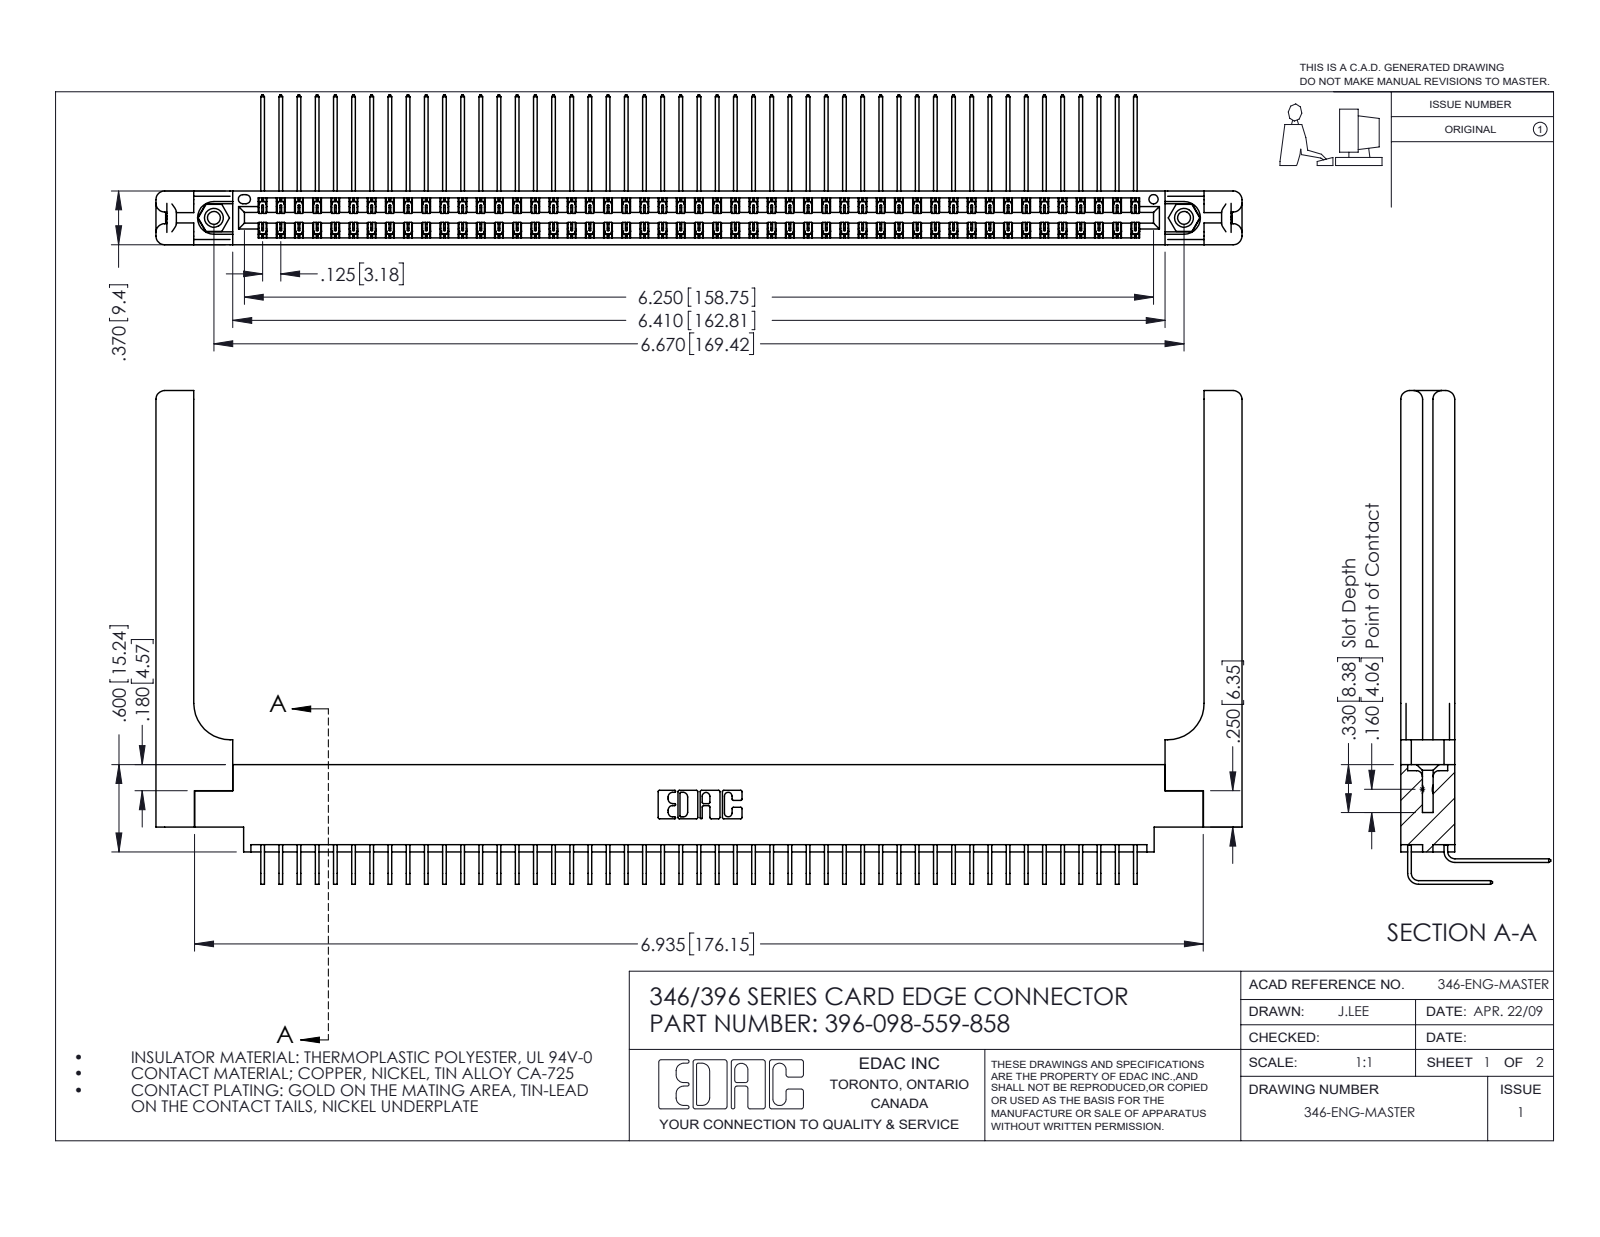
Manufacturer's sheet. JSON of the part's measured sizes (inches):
{"part_name": "396-098-559-858; 345-292-001_559 Tail - 2; 345-250-001_345-250-001-102; 346 Part_0.170 Offset - 0.156 Dia-TH (+2 more)", "step_written_by": "SolidWorks 2016 (CONFIG_CONTROL_DESIGN)", "units": "inches", "bodies": {"solids": 103, "faces": 5674, "planar": 3854, "cylindrical": 1760, "other": 60}, "overall_size": [7.466, 3.393, 1.03], "volume_in3": 1.614, "surface_area_in2": 52.75, "round_holes": [[0.089, 2], [0.125, 2], [0.156, 2], [0.064, 1]], "round_bosses_or_shafts": [[0.155, 2]], "partial_cylinders_radius": [[0.006, 147], [0.01, 22], [0.06, 16], [0.007, 6], [0.031, 6], [0.026, 3], [0.014, 2], [0.022, 2]], "face_to_face_distances": [0.048, 0.37, 0.322, 0.072, 0.025, 0.148, 0.15, 0.25, 0.298, 0.275], "hole_center_spacings": [0.246, 6.461, 6.67]}
